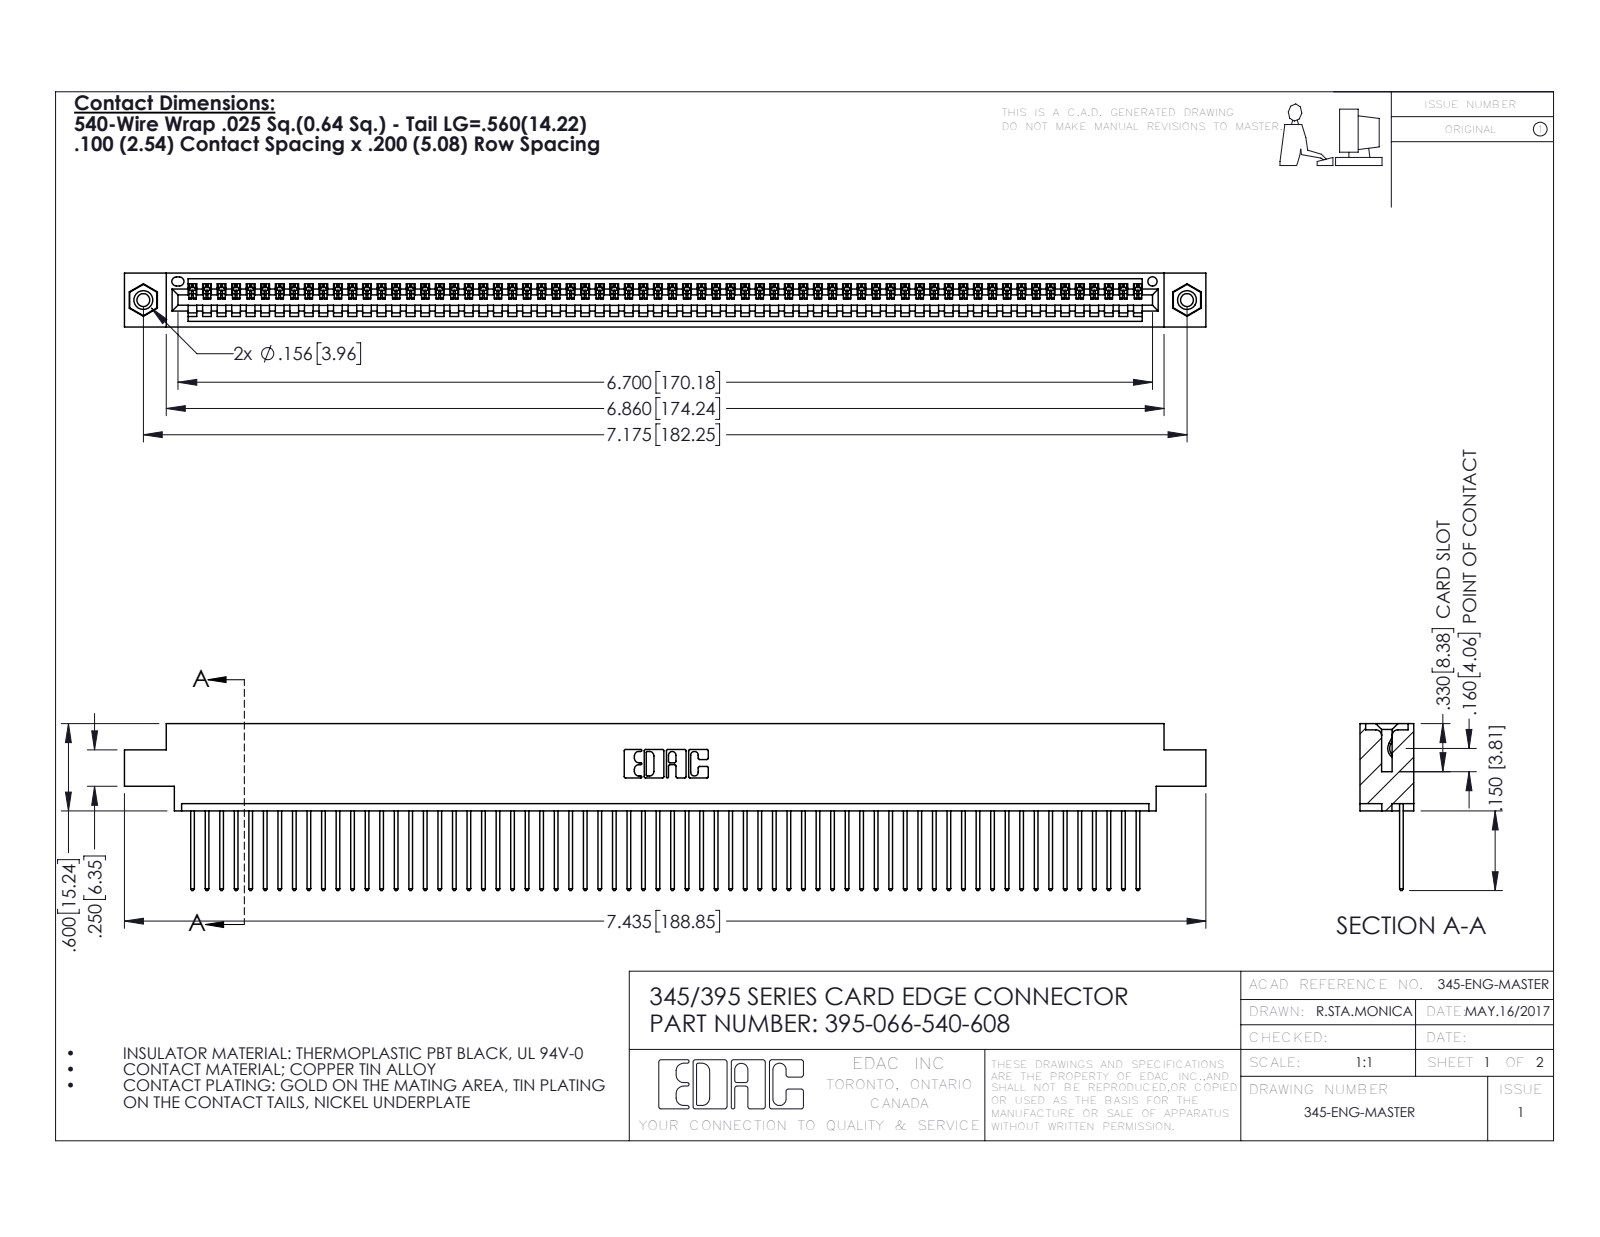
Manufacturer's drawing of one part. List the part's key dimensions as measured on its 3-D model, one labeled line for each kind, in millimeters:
Part name (STEP PRODUCT): 345-292-001_345-293-140; 345 Part_0.170 Offset - 0.156 Dia-TI; 345-250-001_345-250-003-102; 395-066-540-608
STEP written by: SolidWorks 2016 (CONFIG_CONTROL_DESIGN)
Units: millimetres
Bodies: 69 solids, 4018 faces (2756 planar, 1246 cylindrical, 16 other)
Overall size (bounding box): 188.8 × 29.1 × 9.4
Volume: 18 110 mm³ · Surface area: 25 170 mm²
Round holes (diameter × count): ⌀2.3 ×2, ⌀3.2 ×2, ⌀4 ×2, ⌀1.6 ×1
Round bosses / shafts (diameter × count): ⌀3.9 ×2
Partial cylindrical surfaces — rounded edges, fillets, slot ends (radius × count): R0.2 ×132, R0.3 ×132, R0.3 ×22, R0.2 ×6, R0.8 ×6, R0.7 ×3, R0.8 ×2, R1 ×2
Main face-to-face distances: 1.8, 7.6, 9.4, 2.5, 6.9, 0.6, 5.1, 5.7, 4.4, 3.8
Hole centre spacings: 6.9, 176.3, 182.2
